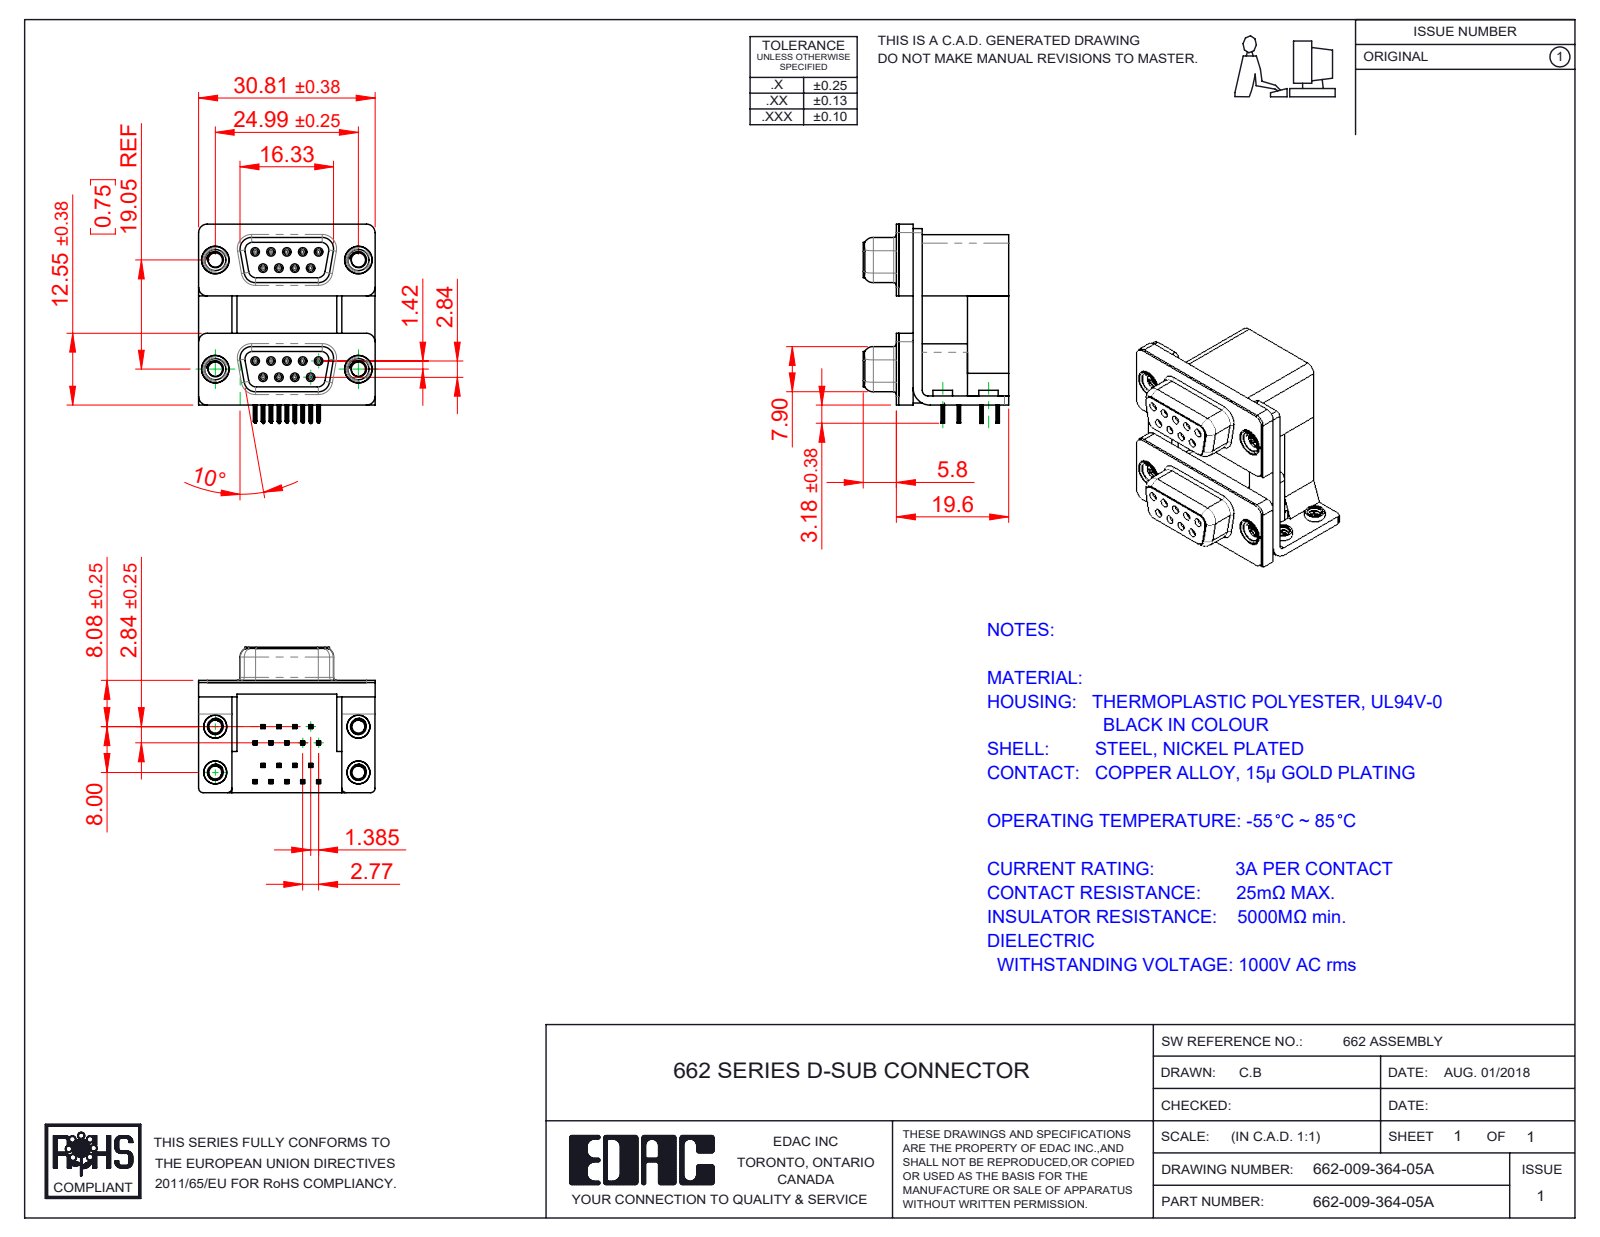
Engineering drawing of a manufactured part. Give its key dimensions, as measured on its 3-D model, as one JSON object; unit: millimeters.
{"part_name": "662-009-364-05A; 662 Housing Lower_09 Contacts; 662 Contact Top Upper_M; 662 Mounting Bracket_ThruM (+8 more)", "step_written_by": "SolidWorks 2020 (CONFIG_CONTROL_DESIGN)", "units": "millimeters", "bodies": {"solids": 33, "faces": 3254, "planar": 1386, "cylindrical": 880, "other": 988}, "overall_size": [34.78, 30.81, 25.4], "volume_mm3": 11323, "surface_area_mm2": 13478, "round_holes": [[0.8, 18], [0.9, 18], [2.26, 4], [2.5, 4], [2.75, 4], [3.2, 4], [3.5, 4], [4, 4], [4.8, 4], [5, 4]], "round_bosses_or_shafts": [[1.2, 18], [4.9, 4], [4.75, 4], [4, 4], [3.9, 4], [3.4, 4]], "partial_cylinders_radius": [[0.1, 144], [0.15, 72], [0.35, 36], [0.34, 18], [1.35, 16], [1.5, 14], [0.28, 8], [0.5, 8]], "face_to_face_distances": [2.5, 0.4, 19.05, 16.7, 19.2, 2.9, 12, 12.4, 7.2, 9.5], "hole_center_spacings": [3.16, 19.25, 2.77, 19.05, 19.84, 21.93, 5.54, 22.28]}
